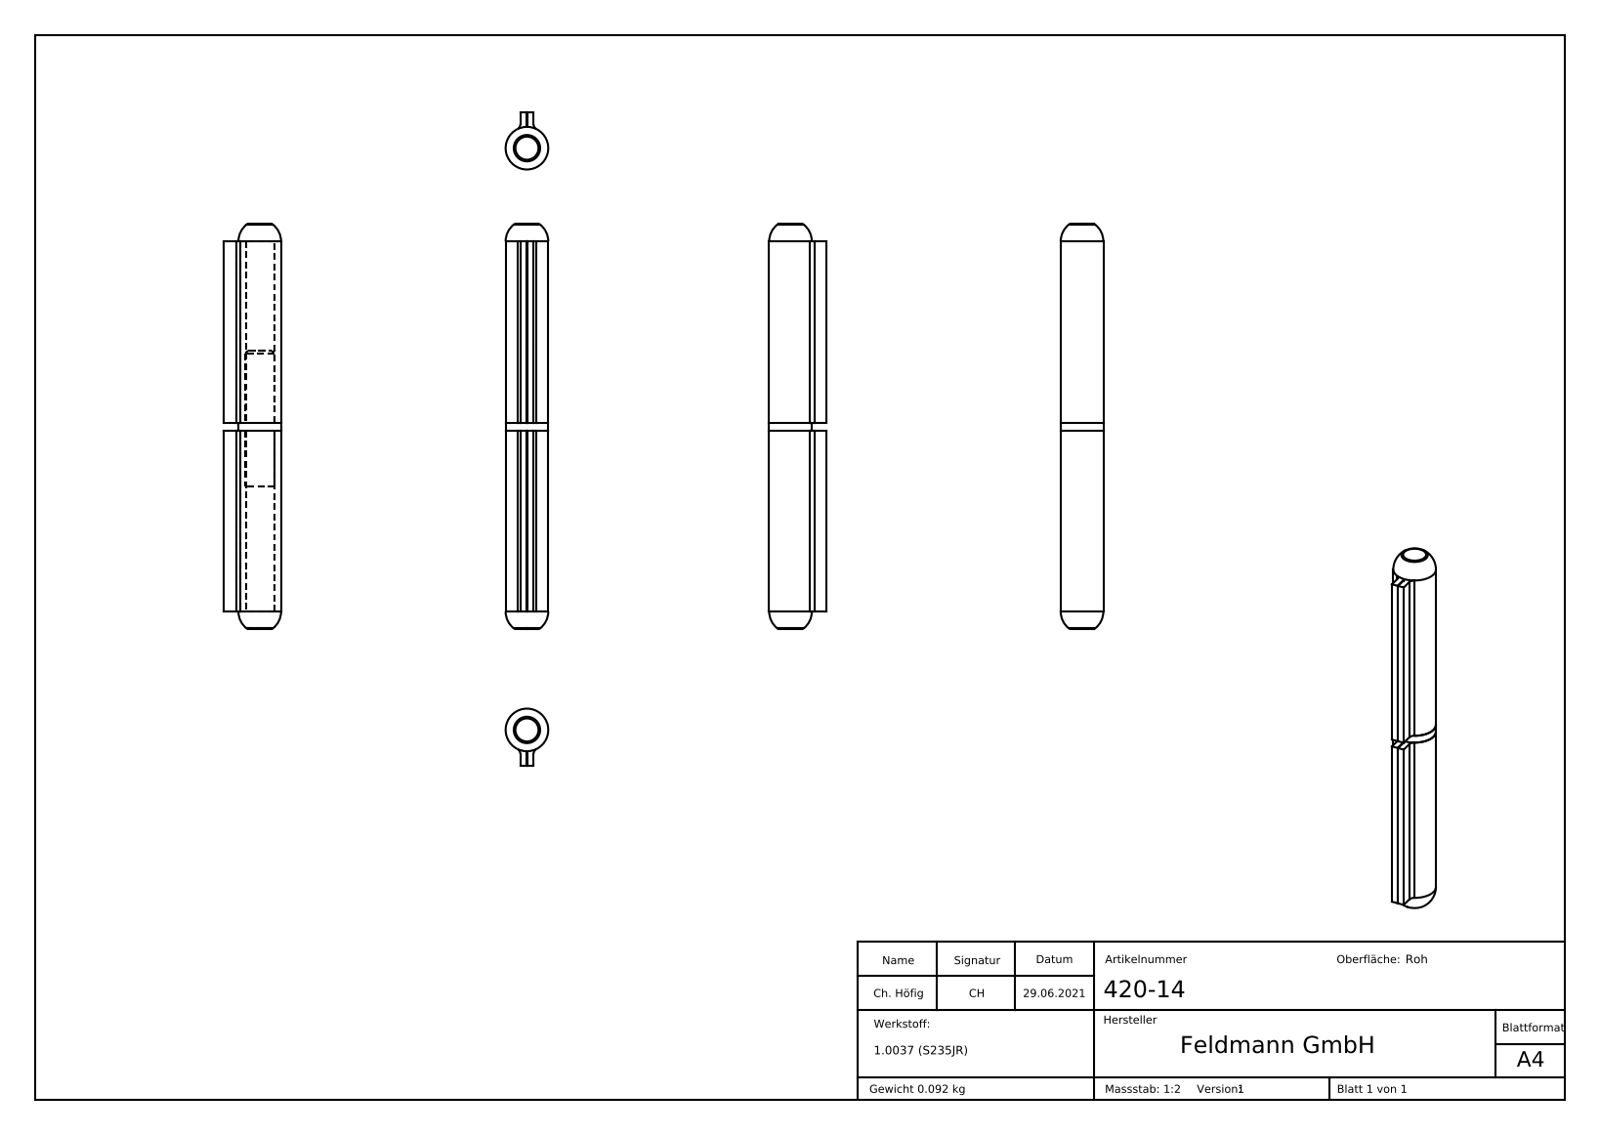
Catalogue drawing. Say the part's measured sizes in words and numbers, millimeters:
The part is named "420-XX Teil1; 420-XX Teil2; 420-XX Teil2_420-14 Teil2; 420-XX Teil1_420-14 Teil1 (+1 more)". Its 3-D file was written by "SolidWorks 2018 (CONFIG_CONTROL_DESIGN)". It is 3 solids with 280 faces: 165 planar, 22 cylindrical and 93 other. Overall it measures 152 by 21.5 by 16 millimeters. Its volume is 24 330 cubic millimeters and its surface area 18 448 square millimeters. Round holes: 1 of diameter 11.2. Round bosses or shafts: 1 of diameter 16, 1 of diameter 10.8. Partial cylindrical surfaces (rounded edges, fillets, slot ends): 2 of radius 2, 2 of radius 4.4. The main face-to-face distances are 2.4, 2.6, 5, 68, 71, 3, 139, 6.5, 74.5, 77.5.
